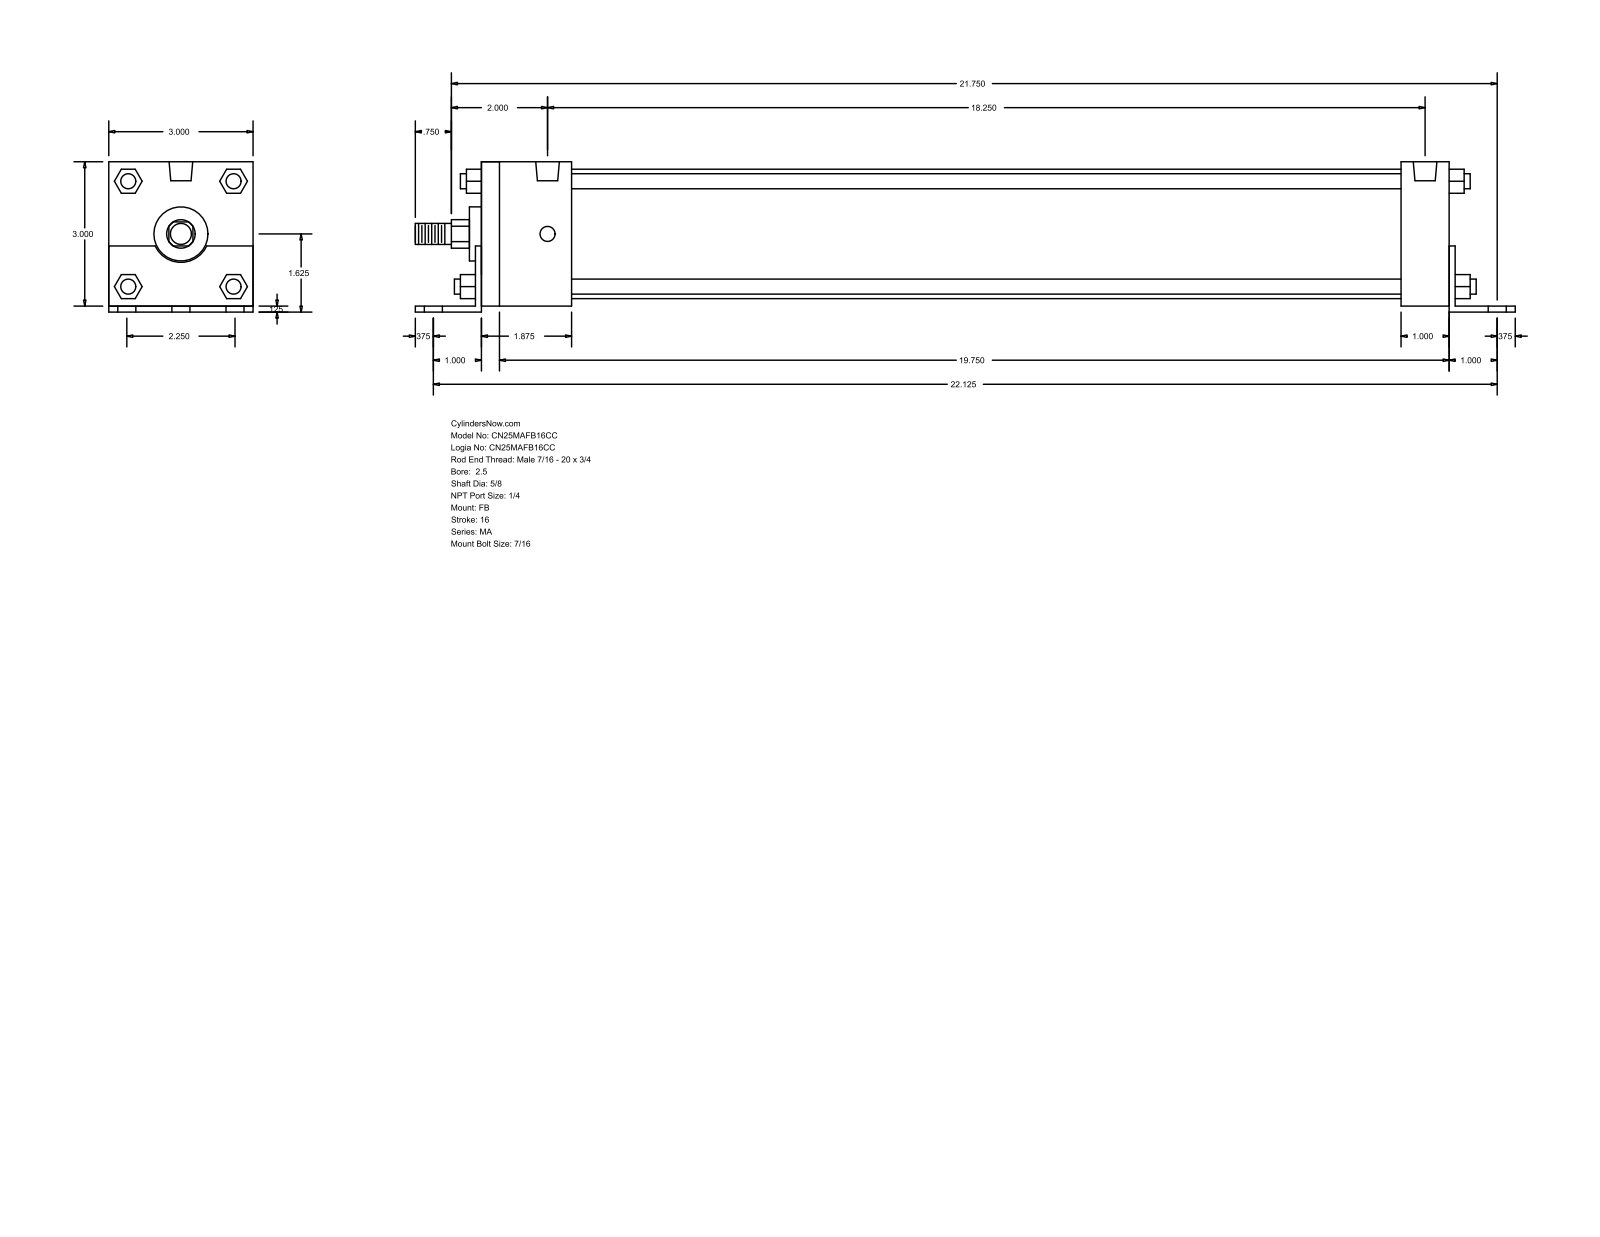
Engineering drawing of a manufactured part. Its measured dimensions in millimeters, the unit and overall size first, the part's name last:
Units: millimetres
Overall size (bounding box): 581.02 × 79.38 × 76.2
Round holes (diameter × count): ⌀11.11 ×6, ⌀7.94 ×4, ⌀12.49 ×2
Round bosses / shafts (diameter × count): ⌀7.94 ×4, ⌀68.33 ×1, ⌀28.57 ×1, ⌀15.88 ×1, ⌀11.11 ×1
Partial cylindrical surfaces — rounded edges, fillets, slot ends (radius × count): R7.54 ×1, R15.05 ×1
Main face-to-face distances: 76.2, 3.17, 79.37, 3.18, 514.35, 511.17, 28.58, 47.62, 25.4, 517.53
Hole centre spacings: 28.57, 562.71, 561.98, 47.62, 57.14, 66.75, 463.55, 502.46
Bodies: 0 solids, 140 faces (105 planar, 35 cylindrical, 0 other)
Part name (STEP PRODUCT): MA_FB__0250_0.625
STEP written by: GSSL Pune (CONFIG_CONTROL_DESIGN)
